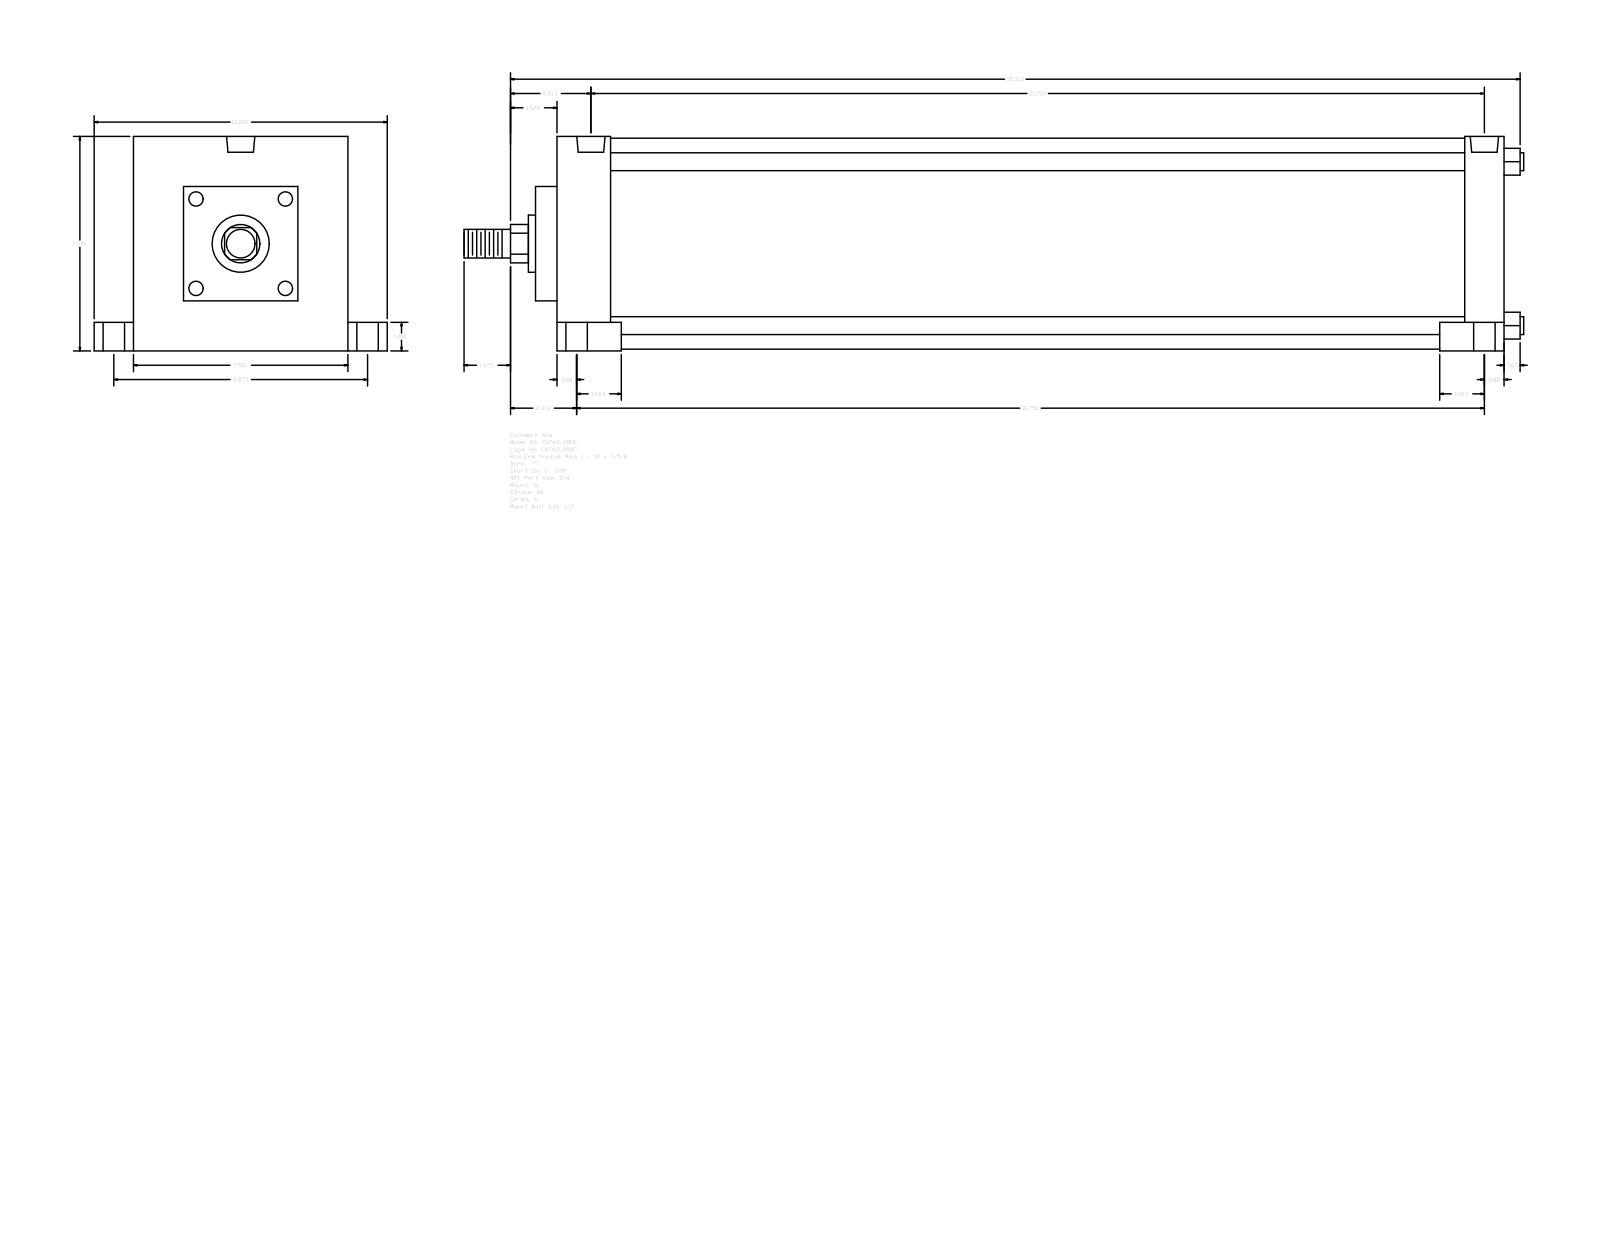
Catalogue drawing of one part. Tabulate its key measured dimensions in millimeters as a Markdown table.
| quantity | value |
| --- | --- |
| part name | A_SL__0700_1.375 |
| STEP written by | GSSL Pune (CONFIG_CONTROL_DESIGN) |
| units | millimeters |
| bodies | 0 solids, 117 faces (85 planar, 32 cylindrical, 0 other) |
| overall size | 941.39 × 260.35 × 190.5 |
| round holes (diameter × count) | 15.08 × 4, 19.05 × 4, 25.4 × 4, 25.12 × 2 |
| round bosses / shafts (diameter × count) | 15.88 × 4, 187.32 × 1, 50.8 × 1, 34.92 × 1, 25.4 × 1 |
| partial cylindrical surfaces (radius × count) | 17.06 × 1 |
| main face-to-face distances | 190.5, 841.38, 19.04, 860.42, 825.5, 66.67, 47.63, 793.75, 806.46, 758.83 |
| hole center spacings | 5.56, 112.71, 112.85, 113.42, 114.18, 225.42, 782.63, 788.19 |
